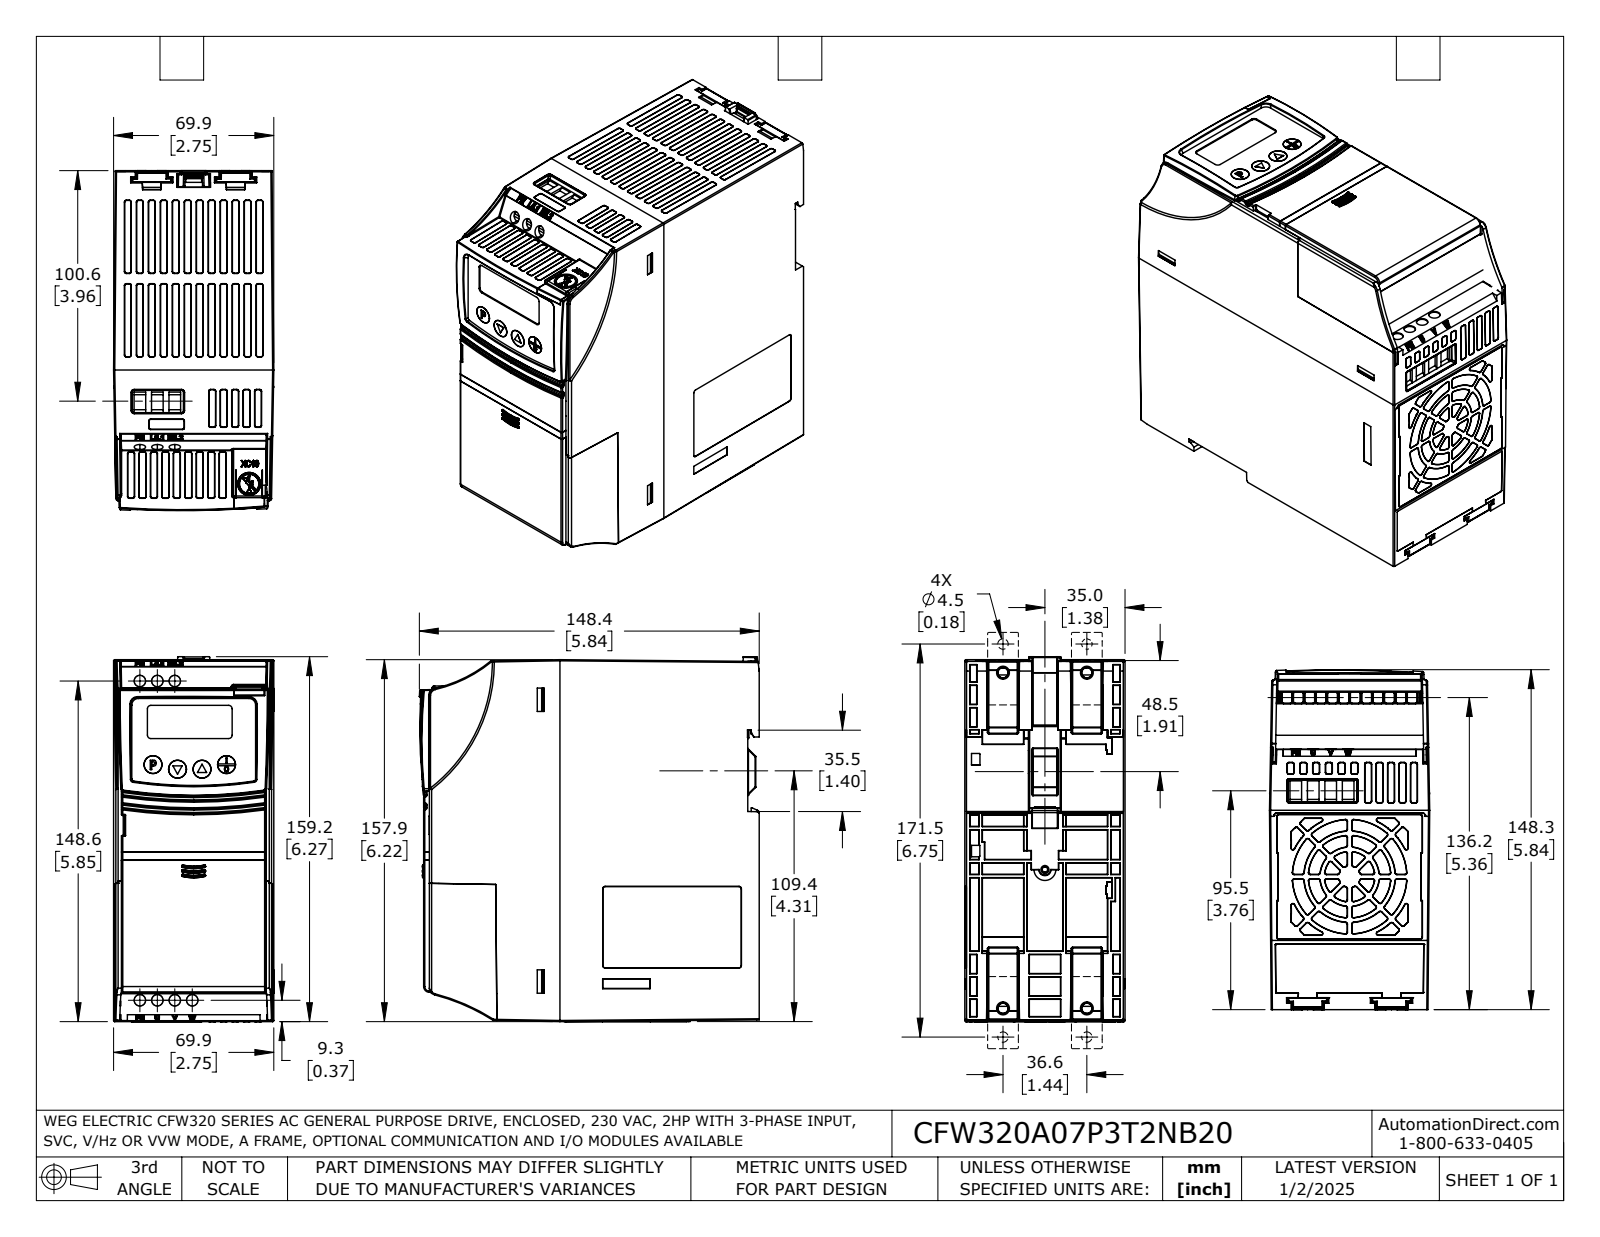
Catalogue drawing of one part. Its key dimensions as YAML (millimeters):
part_name: "CFW320A07P3T2NB20"
step_written_by: "SolidWorks 2021 (AUTOMOTIVE_DESIGN)"
units: millimeters
bodies: {solids: 6, faces: 3715, planar: 1587, cylindrical: 853, other: 1275}
overall_size: [159.2, 148.4, 70]
volume: 249700
surface_area: 199400
round_holes:
  - {diameter: 5, count: 3}
partial_cylinders:
  - {radius: 0.3, count: 327}
  - {radius: 0.5, count: 150}
  - {radius: 1, count: 13}
  - {radius: 0.8, count: 5}
  - {radius: 3, count: 3}
  - {radius: 0.3, count: 2}
  - {radius: 2.5, count: 1}
  - {radius: 3.2, count: 1}
face_to_face_distances: [1.8, 1.4, 0.5, 1.3, 152.4, 135.4, 134, 141.5, 140.1, 6.1]
hole_center_spacings: [7.6, 15.2]
